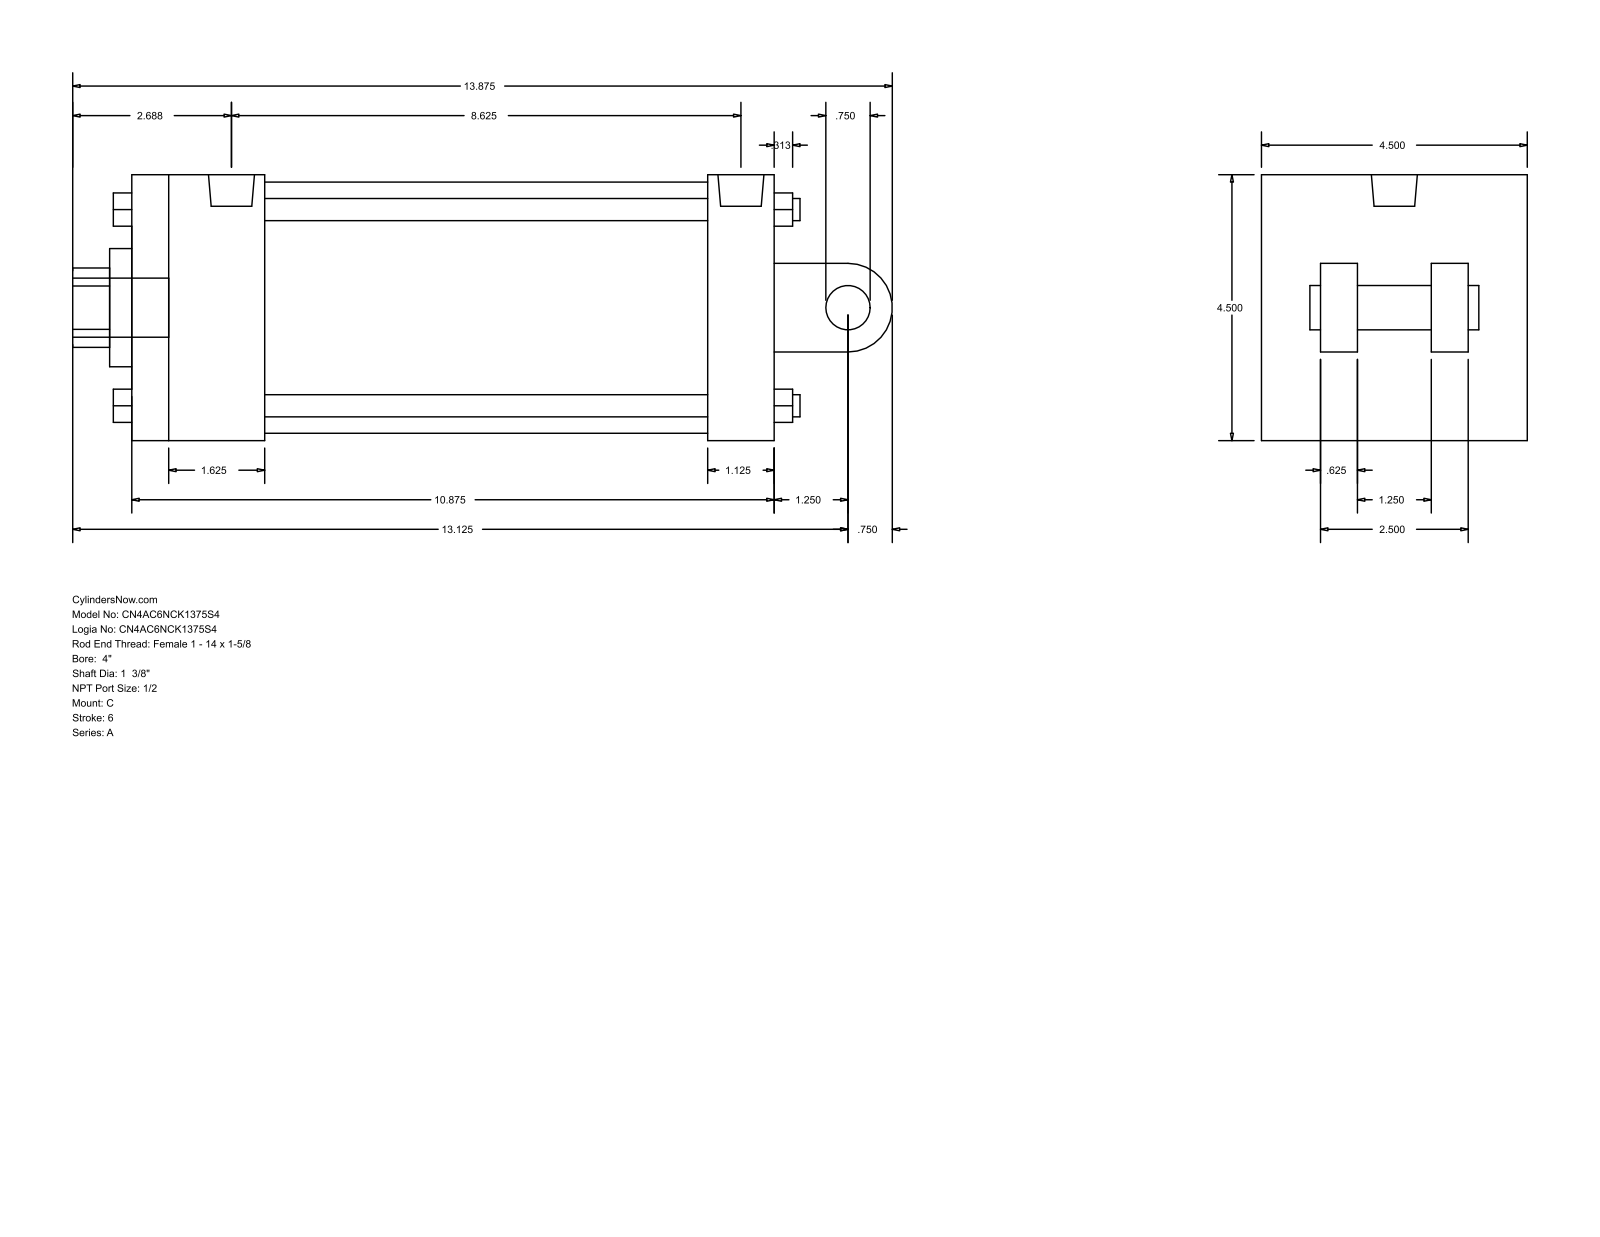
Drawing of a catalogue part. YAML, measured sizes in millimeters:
part_name: "A_C__0400_1.375"
step_written_by: "GSSL Pune (CONFIG_CONTROL_DESIGN)"
units: millimeters
bodies: {solids: 0, faces: 135, planar: 102, cylindrical: 33, other: 0}
overall_size: [352.43, 114.3, 114.3]
round_holes:
  - {diameter: 8.73, count: 2}
  - {diameter: 19.77, count: 1}
  - {diameter: 34.92, count: 1}
  - {diameter: 50.8, count: 1}
  - {diameter: 107.95, count: 1}
round_bosses_or_shafts:
  - {diameter: 9.53, count: 4}
  - {diameter: 8.73, count: 2}
  - {diameter: 25.4, count: 1}
  - {diameter: 19.77, count: 1}
  - {diameter: 19.05, count: 1}
partial_cylinders:
  - {radius: 17.06, count: 1}
  - {radius: 19.05, count: 1}
face_to_face_distances: [114.3, 276.22, 73.03, 28.57, 247.65, 57.15, 190.5, 219.07, 15.87, 41.27]
hole_center_spacings: [3.18]
